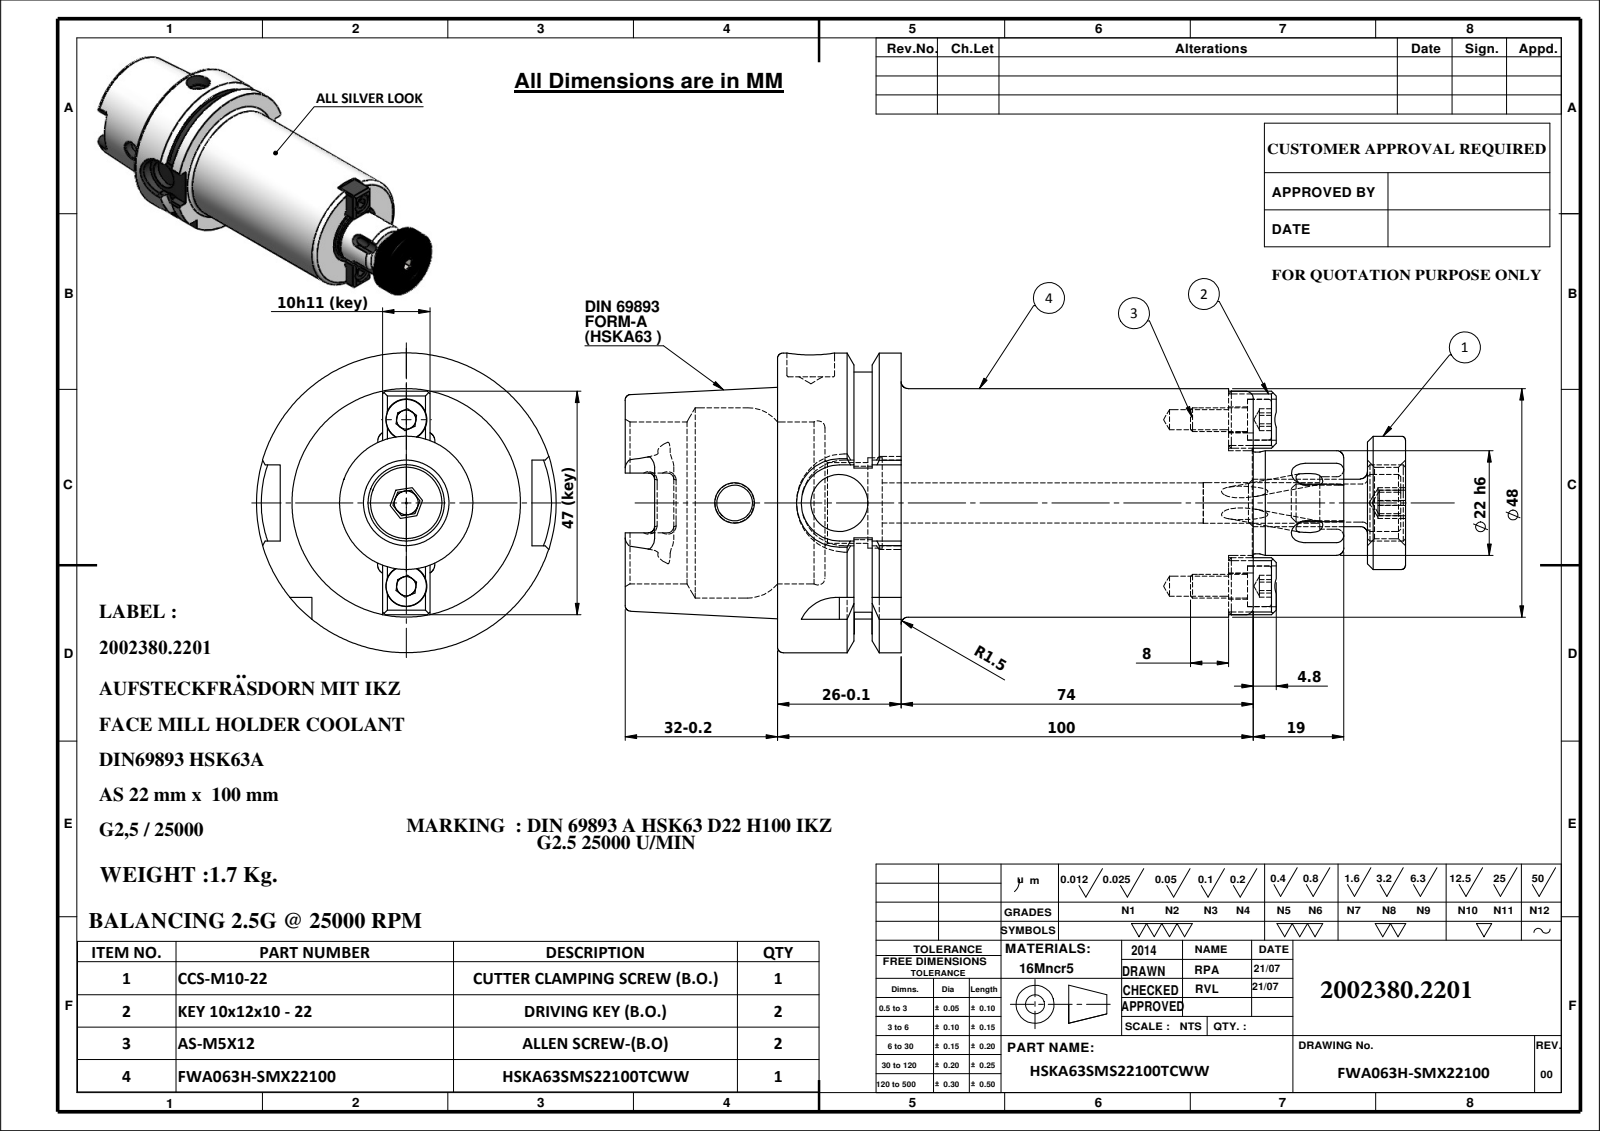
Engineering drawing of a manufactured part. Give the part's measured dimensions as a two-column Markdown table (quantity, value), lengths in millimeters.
| quantity | value |
| --- | --- |
| part name | CCS-M10-22-1 LONG; CCS-M10-22-2; 9163A-AS522100; HSKA63SMS22100TCWW (+4 more) |
| STEP written by | SolidWorks 2009 (CONFIG_CONTROL_DESIGN) |
| units | millimeters |
| bodies | 7 solids, 385 faces (164 planar, 101 cylindrical, 120 other) |
| overall size | 164 × 63 × 63 |
| volume | 223 066 mm³ |
| surface area | 44 274 mm² |
| round holes (diameter × count) | 3 × 4, 4.2 × 2, 5.4 × 2, 8.6 × 2, 7.5 × 1, 8.4 × 1, 8.5 × 1, 10 × 1, 11 × 1, 12 × 1, 15 × 1, 17 × 1 |
| round bosses / shafts (diameter × count) | 8.5 × 2, 5 × 2, 63 × 1, 55 × 1, 48 × 1, 28 × 1, 22 × 1, 21.4 × 1 |
| partial cylindrical surfaces (radius × count) | 2 × 8, 1.3 × 6, 2.88 × 4, 8 × 2, 9 × 1 |
| main face-to-face distances | 100, 26, 74, 32, 132, 10, 16, 90, 122, 106 |
| hole center spacings | 17.5, 22, 35 |
